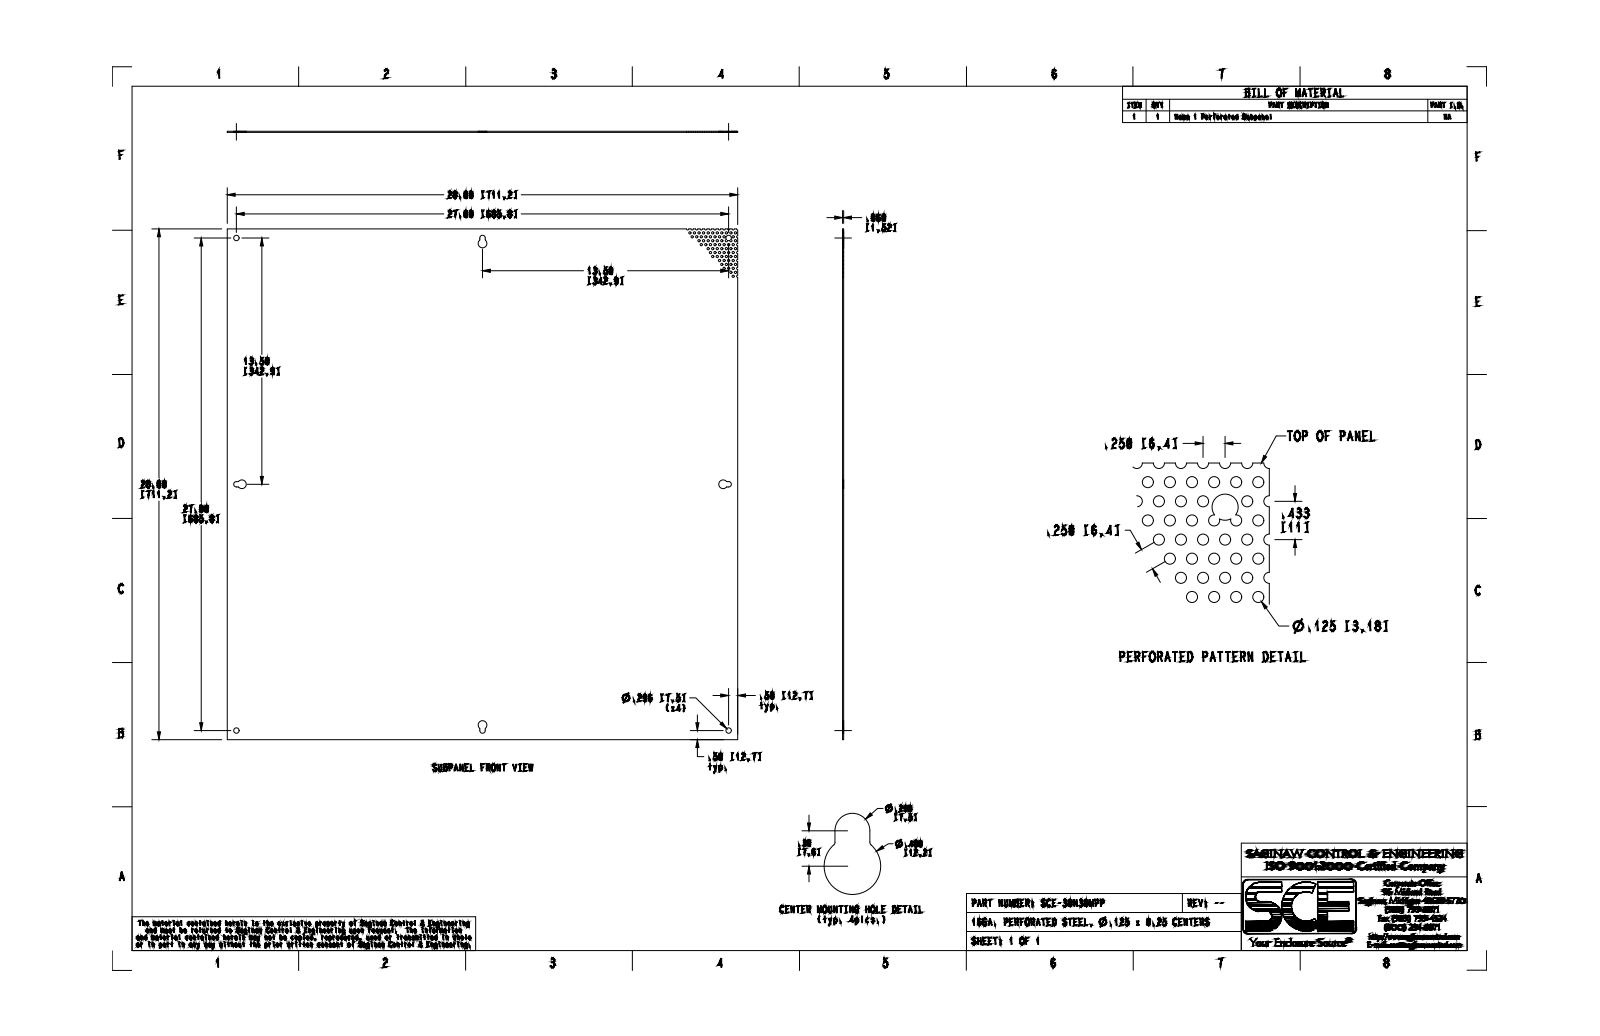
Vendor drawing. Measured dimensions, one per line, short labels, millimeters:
name: SCE-30N30MPP
written by: SolidWorks 2019 (CONFIG_CONTROL_DESIGN)
unit: mm
bodies: 1 solid, 140 faces (31 planar, 109 cylindrical, 0 other)
size: 711.2 × 711.2 × 1.5
volume: 768 700 mm³; area: 1 015 000 mm²
holes: 70× ⌀3.2, 4× ⌀7.5
rounds: 18× R1.6, 8× R0.8, 4× R3.8, 4× R6.1
face distances: 1.5, 711.2, 351.8, 359.4, 7.5
hole spacings: 6.4, 16.8, 12.7, 11, 11, 33.6, 22.9, 27.7
